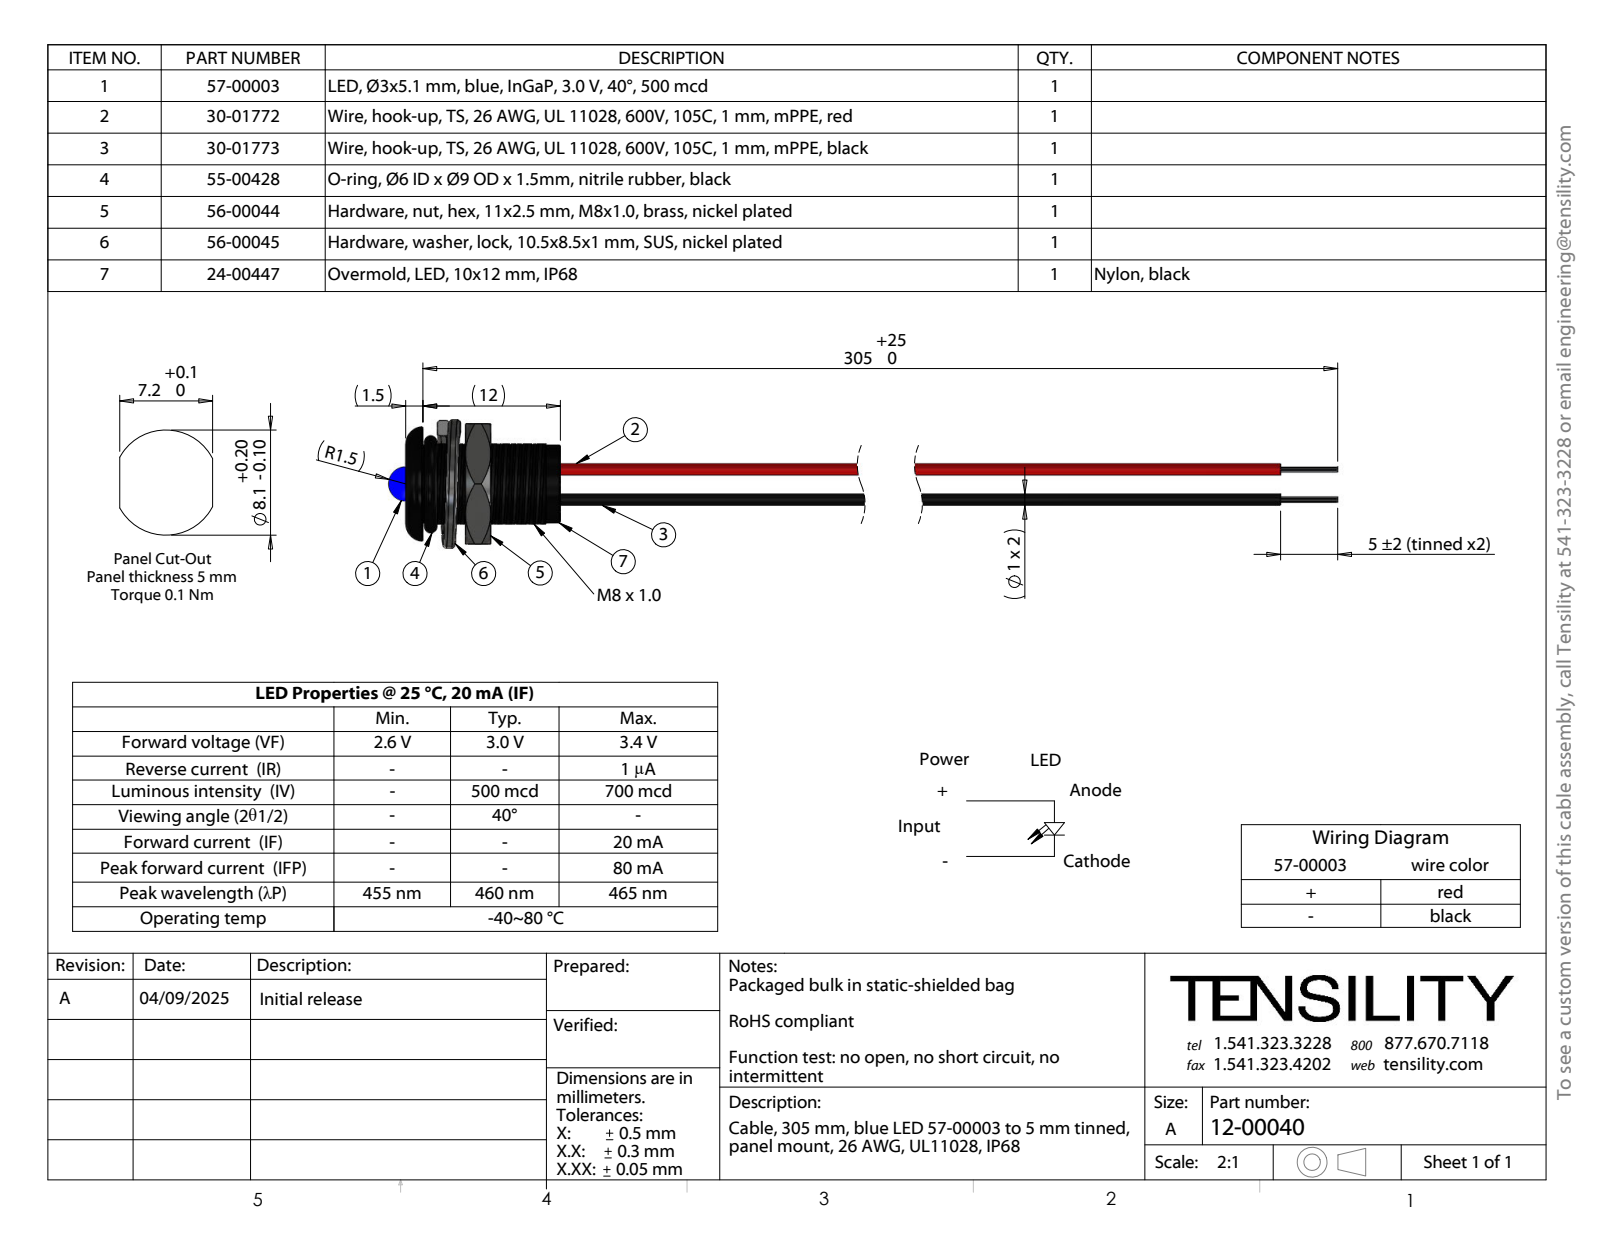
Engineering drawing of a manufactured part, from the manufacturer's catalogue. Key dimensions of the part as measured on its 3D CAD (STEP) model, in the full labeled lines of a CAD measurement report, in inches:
Part name (STEP PRODUCT): 56-00044; 55-00428; 12-00040; 30-01772_stripped and tinned (+4 more)
STEP written by: SolidWorks 2021 (CONFIG_CONTROL_DESIGN)
Units: inches
Bodies: 57 solids, 555 faces (186 planar, 246 cylindrical, 123 other)
Overall size (bounding box): 6.693 × 0.477 × 0.441
Volume: 0.061 in³ · Surface area: 9.157 in²
Round holes (diameter × count): ⌀0.039 ×2
Round bosses / shafts (diameter × count): ⌀0.039 ×2, ⌀0.02 ×2, ⌀0.268 ×1, ⌀0.118 ×1
Partial cylindrical surfaces — rounded edges, fillets, slot ends (radius × count): R0.137 ×1, R0.157 ×1
Main face-to-face distances: 0.059, 0.531, 0.472, 0.413, 0.205, 0.146, 0.326, 0.292, 0.233, 0.087
Hole centre spacings: 0.014, 0.015, 0.013, 0.098, 0.099, 0.096, 0.096, 0.101
